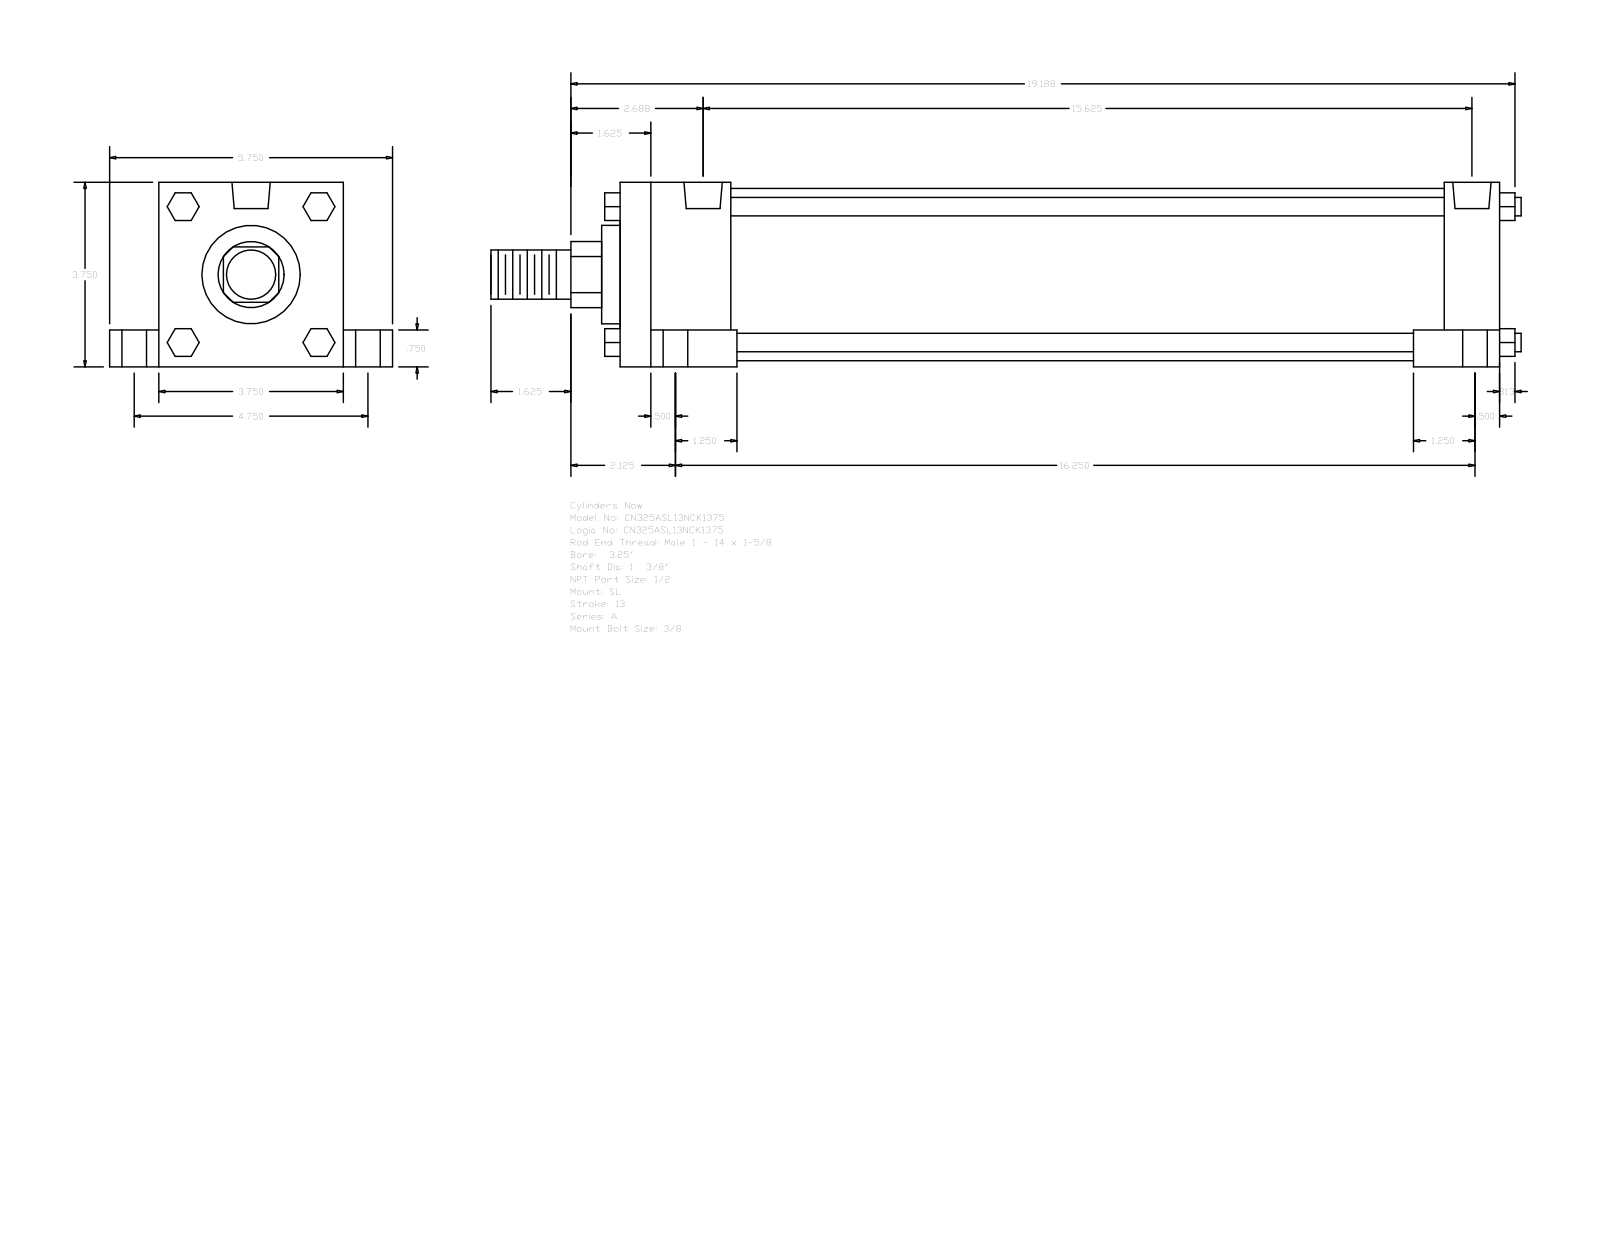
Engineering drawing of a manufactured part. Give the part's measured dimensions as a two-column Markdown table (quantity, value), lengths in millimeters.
| quantity | value |
| --- | --- |
| part name | A_SL__0325_1.375 |
| STEP written by | GSSL Pune (CONFIG_CONTROL_DESIGN) |
| units | millimeters |
| bodies | 0 solids, 150 faces (114 planar, 36 cylindrical, 0 other) |
| overall size | 531.81 × 146.05 × 95.25 |
| round holes (diameter × count) | 8.73 × 4, 12.7 × 4, 19.05 × 4, 19.77 × 2 |
| round bosses / shafts (diameter × count) | 9.53 × 4, 88.9 × 1, 50.8 × 1, 34.92 × 1, 25.4 × 1 |
| partial cylindrical surfaces (radius × count) | 17.06 × 1 |
| main face-to-face distances | 95.24, 454.03, 25.41, 120.65, 19.05, 76.19, 57.15, 28.58, 425.45, 368.3 |
| hole center spacings | 3.18, 60.35, 60.52, 62, 62.81, 120.66, 390.52, 393.7 |
